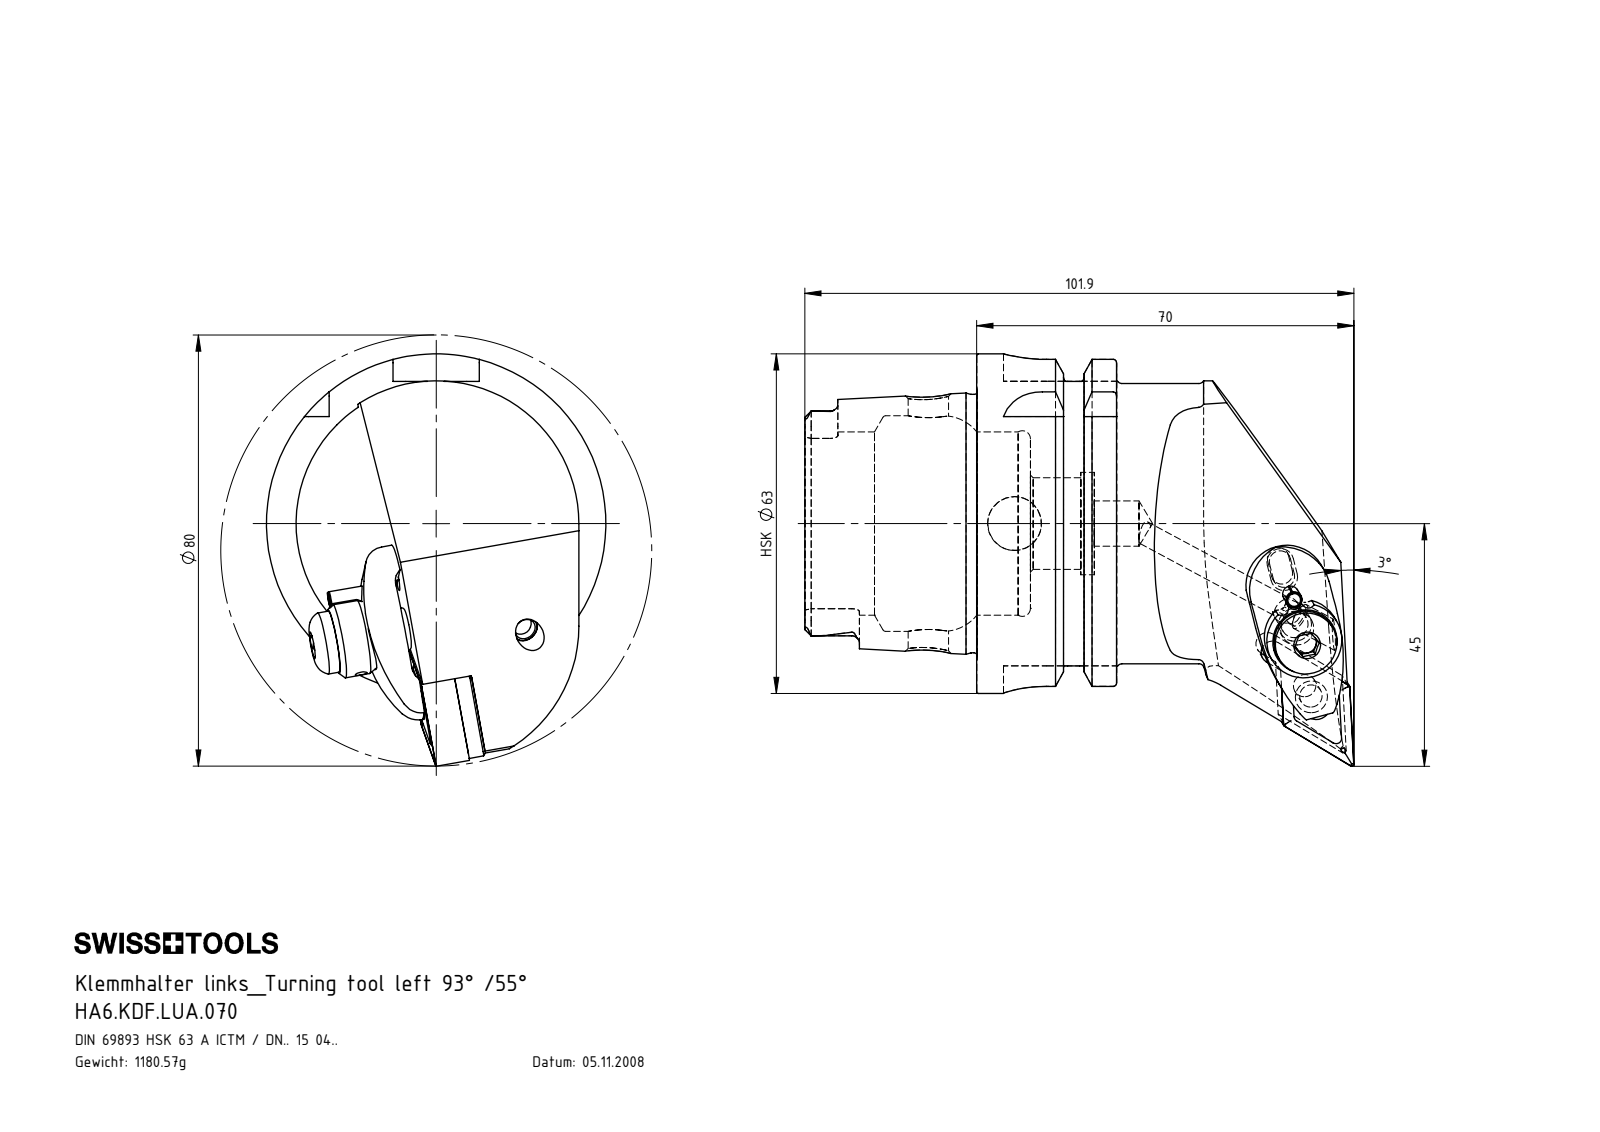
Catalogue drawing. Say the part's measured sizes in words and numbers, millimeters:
The part is named "WDF-ER2.101.003_A; HA6-KDF.LUA.070_C; HA6.KDF.LUA.070; ISO 13337 - 3 x 12_PreviewCfg (+7 more)". Its 3-D file was written by "SolidWorks 2017 (AUTOMOTIVE_DESIGN)". It is 11 solids with 470 faces: 126 planar, 153 cylindrical and 191 other. Overall it measures 101.9 by 76.5 by 63 millimeters. Its volume is 151 349 cubic millimeters and its surface area 35 326 square millimeters. Round holes: 3 of diameter 2, 2 of diameter 4.2, 2 of diameter 5, 2 of diameter 7, 1 of diameter 2.4, 1 of diameter 3, 1 of diameter 4, 1 of diameter 5.16, 1 of diameter 6.2, 1 of diameter 6.4, 1 of diameter 7.5, 1 of diameter 8.4. Round bosses or shafts: 2 of diameter 5, 2 of diameter 3, 1 of diameter 63, 1 of diameter 54.95, 1 of diameter 52, 1 of diameter 47.94, 1 of diameter 14, 1 of diameter 11.5. Partial cylindrical surfaces (rounded edges, fillets, slot ends): 6 of radius 0.39, 6 of radius 1.4, 4 of radius 0.4, 4 of radius 1, 4 of radius 8, 3 of radius 0.69, 3 of radius 0.69, 3 of radius 1.5. The main face-to-face distances are 25.95, 16, 9.95, 12.32, 31.9, 41.85, 57.85, 6.01, 52.8, 3.18. The hole center spacings are 7.99, 8, 8.2, 23, 14.8, 14.81, 14.99, 15.
